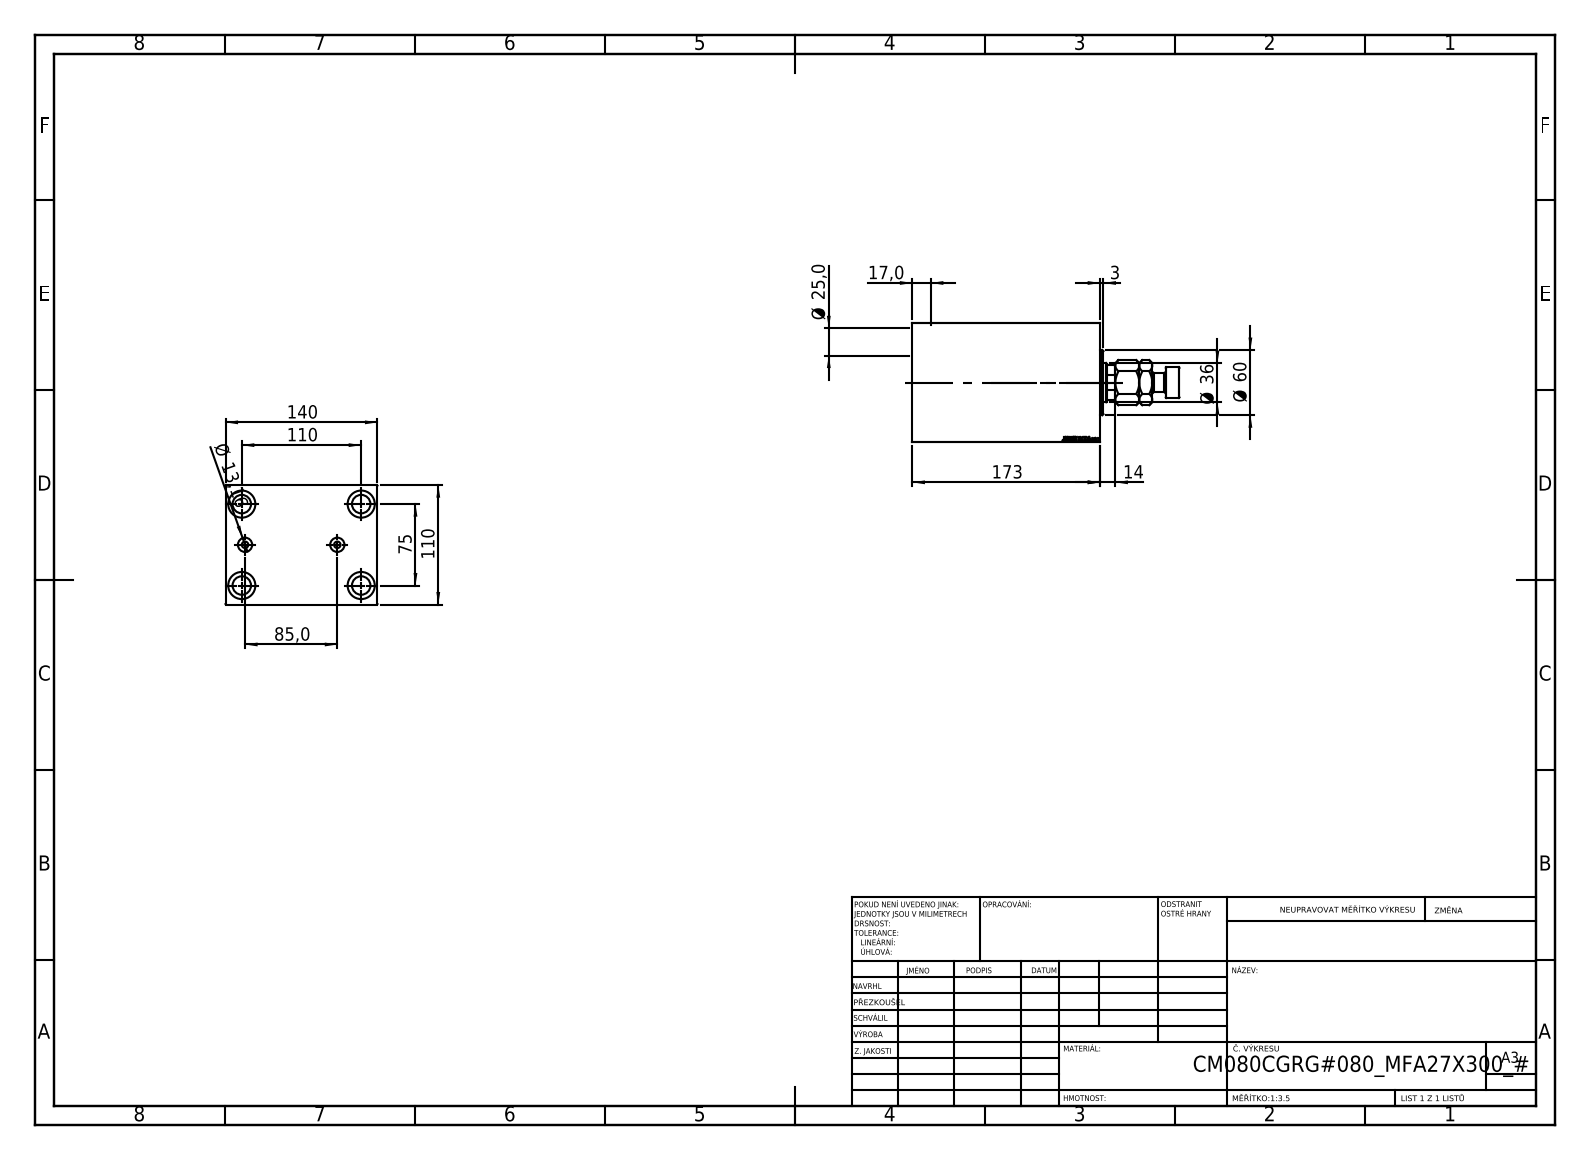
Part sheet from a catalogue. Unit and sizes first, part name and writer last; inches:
Units: inches
Overall size (bounding box): 9.685 × 5.512 × 4.331
Round holes (diameter × count): ⌀0.669 ×4, ⌀0.984 ×4, ⌀0.236 ×2, ⌀0.518 ×2, ⌀1.004 ×1, ⌀1.417 ×1, ⌀1.555 ×1, ⌀3.15 ×1, ⌀3.228 ×1, ⌀3.425 ×1
Round bosses / shafts (diameter × count): ⌀2.362 ×1, ⌀1.102 ×1, ⌀0.709 ×1
Partial cylindrical surfaces — rounded edges, fillets, slot ends (radius × count): R0.689 ×1
Main face-to-face distances: 4.331, 5.512, 6.811, 5.984, 0.827, 0.551, 6.26, 5.433, 3.701, 3.15
Hole centre spacings: 2.621, 1.481, 1.712, 2.953, 3.766, 4.331, 4.464, 5.242
Volume: 133.8 in³ · Surface area: 406.3 in²
Bodies: 4 solids, 912 faces (424 planar, 62 cylindrical, 426 other)
Part name (STEP PRODUCT): V450CM_VC_B; V450CM_C_Body; V450CM_C_VCP; MFA
STEP written by: SolidWorks 2019 (CONFIG_CONTROL_DESIGN)
